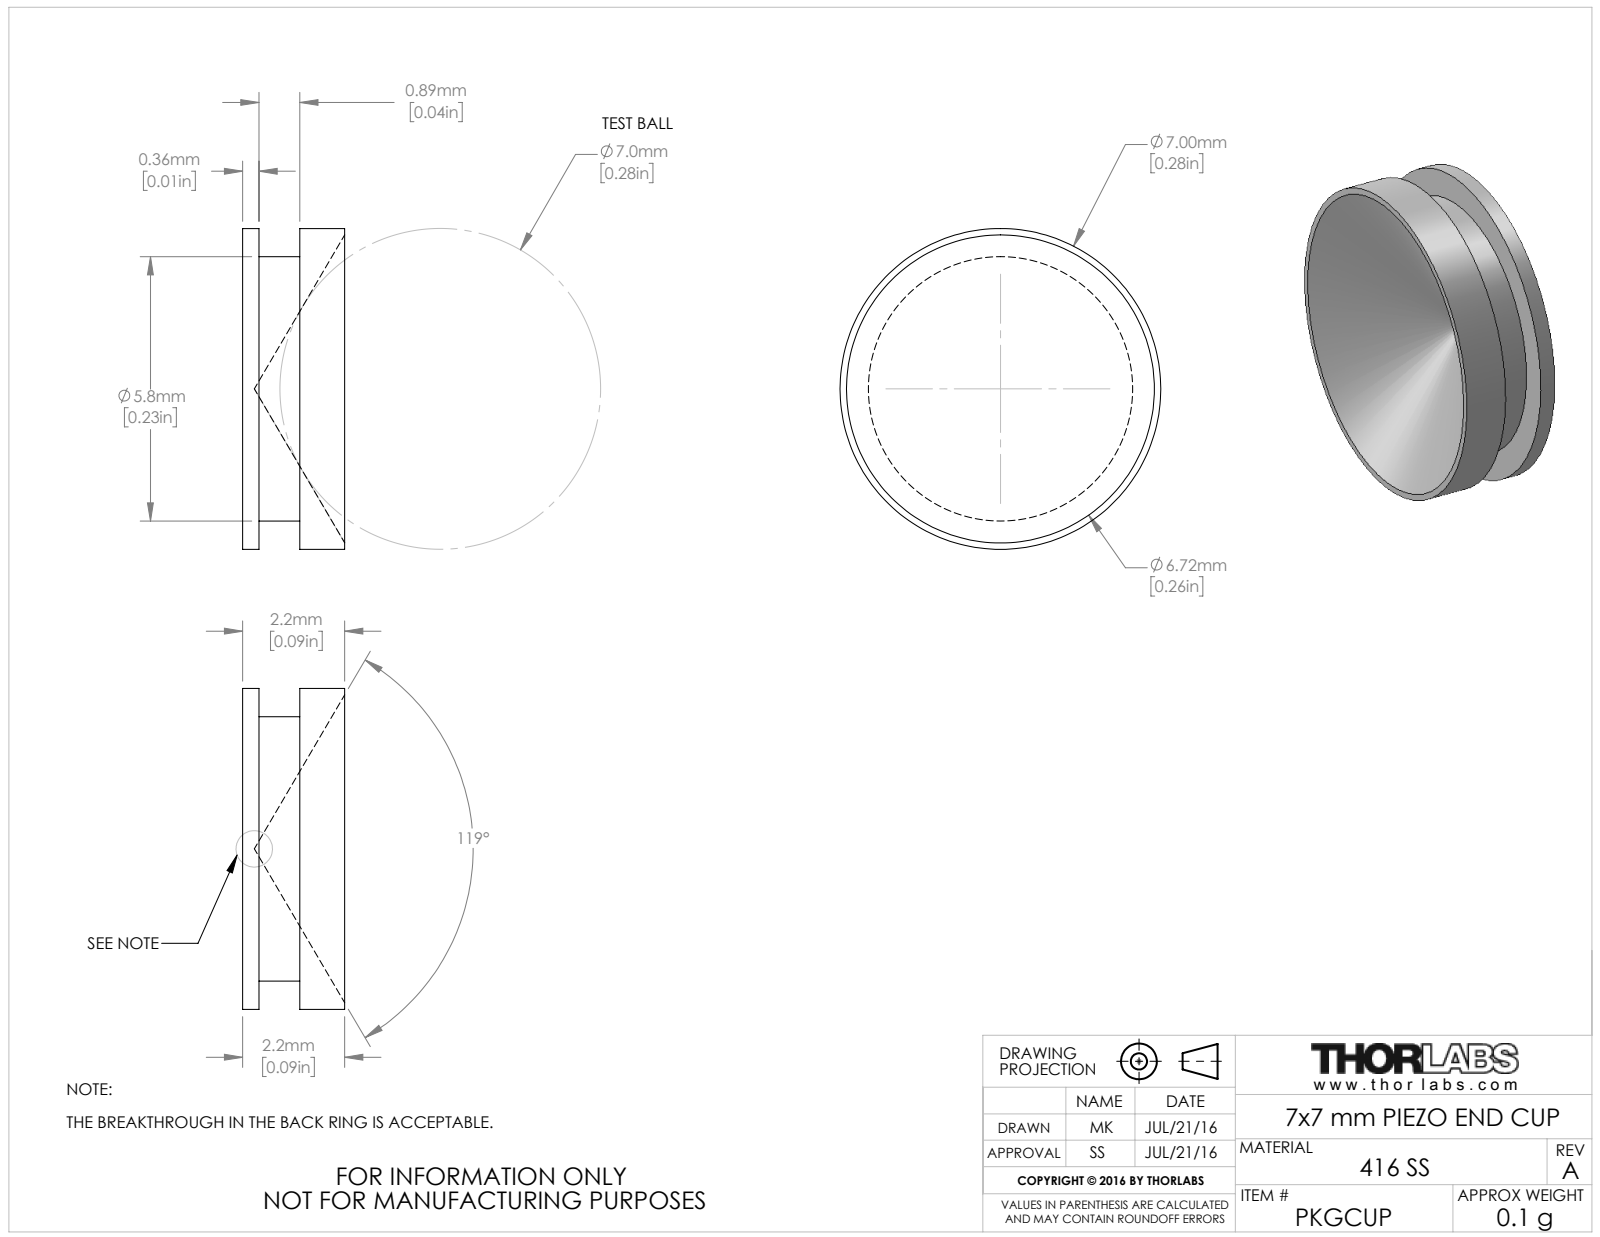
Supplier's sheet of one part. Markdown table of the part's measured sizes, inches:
| quantity | value |
| --- | --- |
| part name | CTN002776 |
| STEP written by | SolidWorks 2016 (AUTOMOTIVE_DESIGN) |
| units | inches |
| bodies | 1 solid, 12 faces (4 planar, 6 cylindrical, 2 other) |
| overall size | 0.276 × 0.276 × 0.088 |
| volume | 0.003 in³ |
| surface area | 0.237 in² |
| round bosses / shafts (diameter × count) | 0.276 × 1, 0.227 × 1 |
| main face-to-face distances | 0.014, 0.049, 0.035, 0.087, 0.073, 0.039 |
